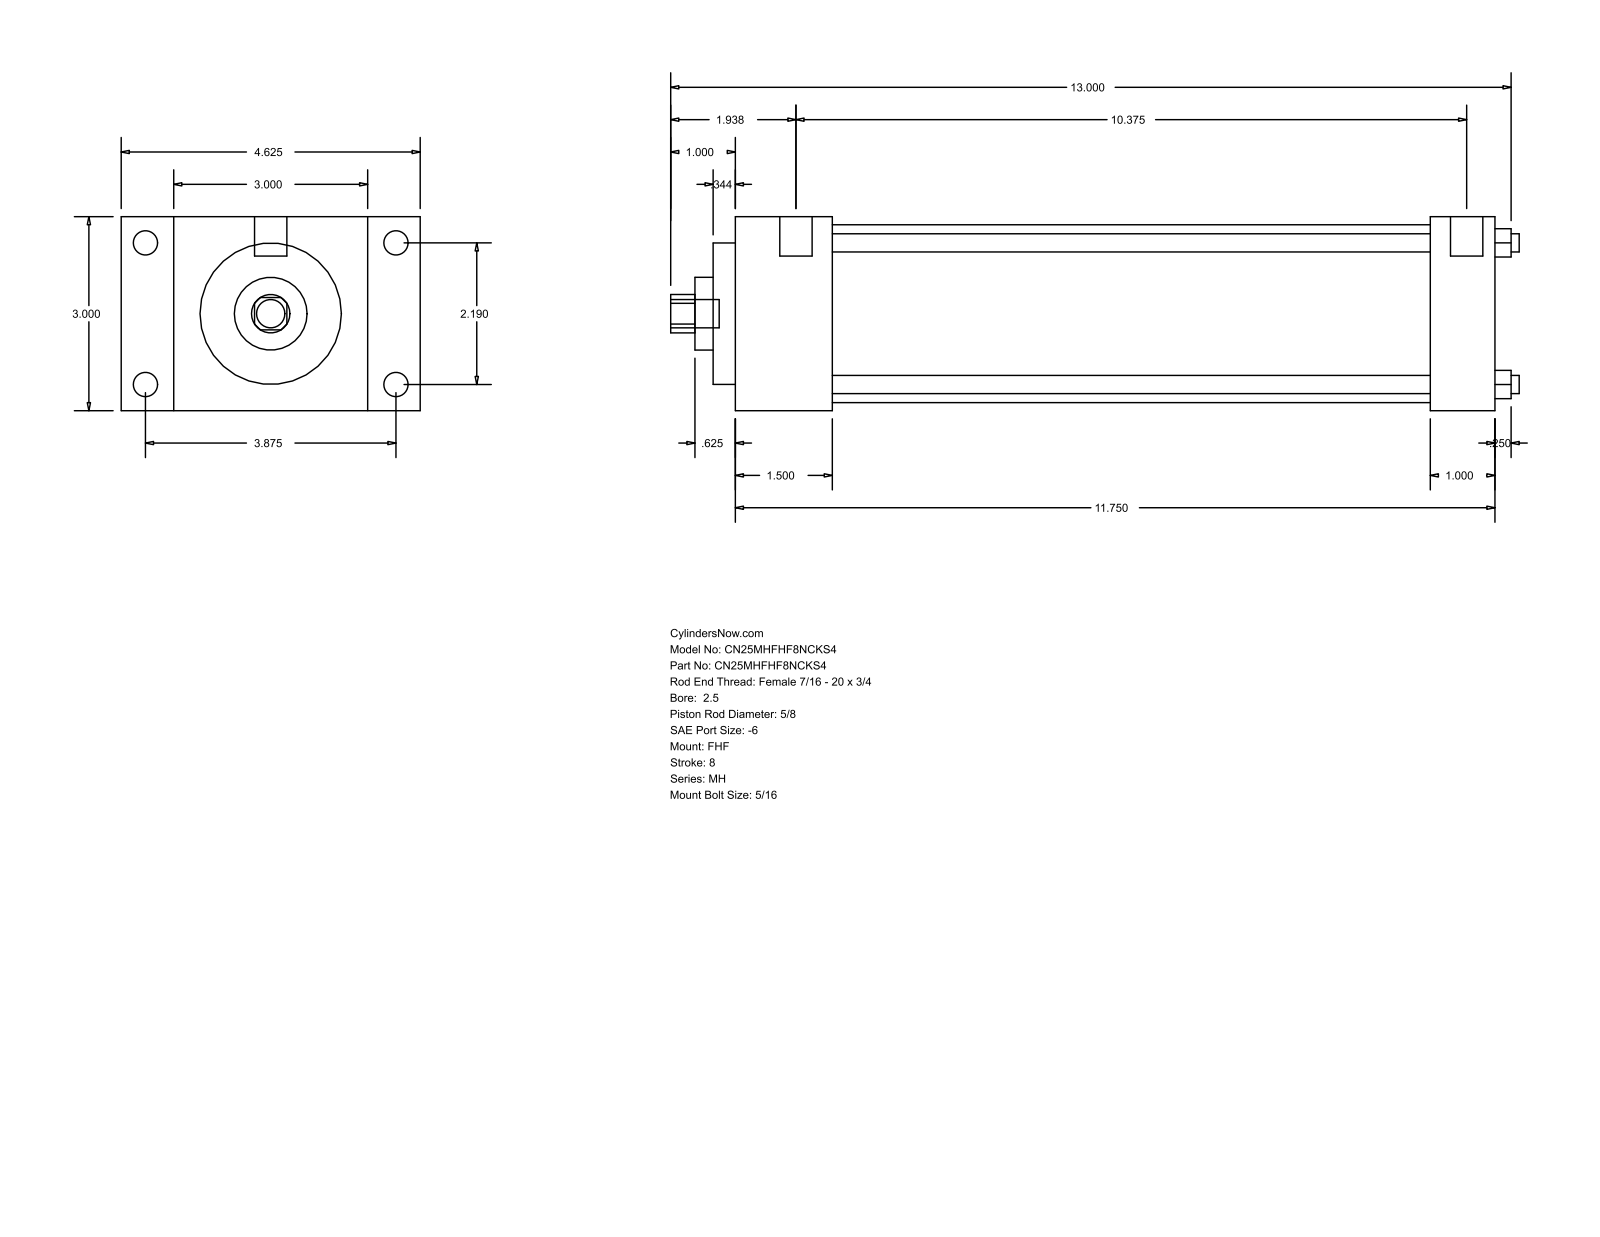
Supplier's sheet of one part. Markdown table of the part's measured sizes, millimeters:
| quantity | value |
| --- | --- |
| part name | MH_FHF__0250_0.625 |
| STEP written by | GSSL Pune (CONFIG_CONTROL_DESIGN) |
| units | millimeters |
| bodies | 0 solids, 90 faces (61 planar, 29 cylindrical, 0 other) |
| overall size | 333.38 × 117.47 × 76.2 |
| round holes (diameter × count) | 7.14 × 4, 15.88 × 1, 28.57 × 1, 55.55 × 1, 69.85 × 1 |
| round bosses / shafts (diameter × count) | 9.53 × 4, 5.56 × 4, 12.7 × 2, 11.11 × 1 |
| partial cylindrical surfaces (radius × count) | 7.54 × 1 |
| main face-to-face distances | 76.2, 298.45, 38.1, 260.35, 20.64, 96.84, 117.48, 25.4, 273.05, 234.95 |
| hole center spacings | 39.33, 55.62, 78.66 |
